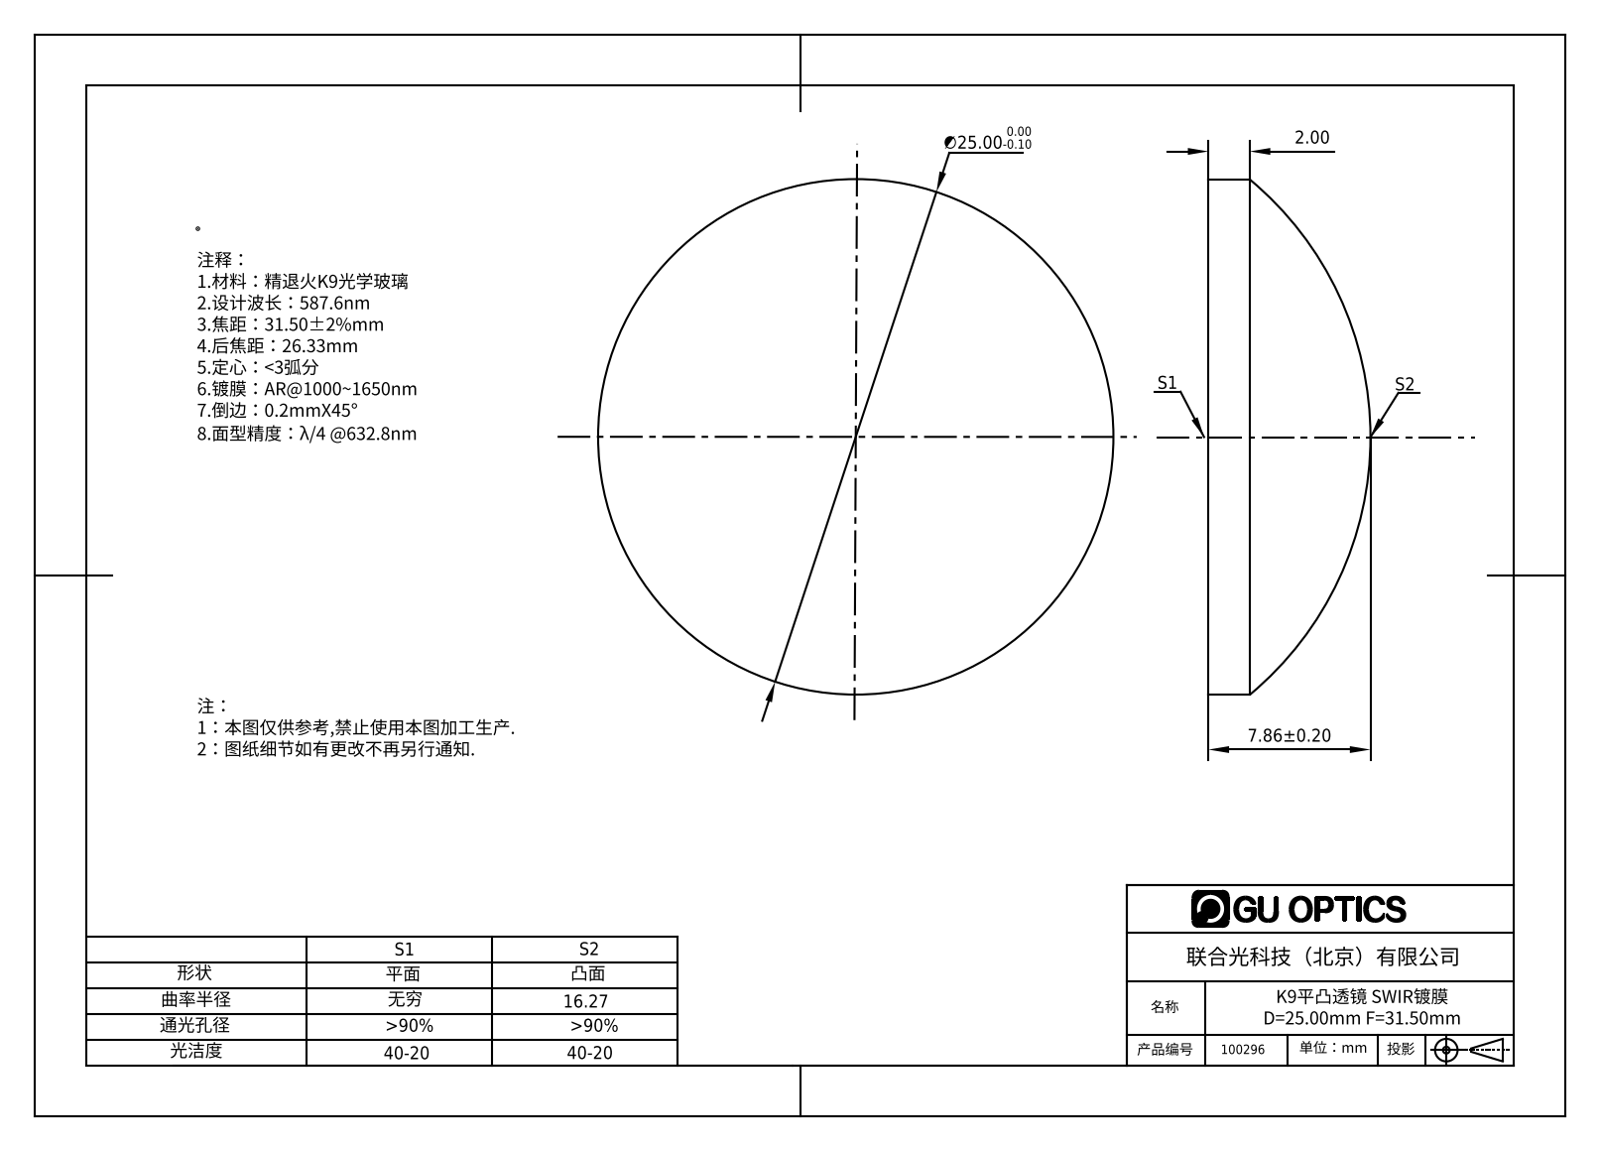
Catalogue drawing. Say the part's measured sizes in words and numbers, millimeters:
The part is named "100124". Its 3-D file was written by "SolidWorks 2016 (AUTOMOTIVE_DESIGN)". It is 1 solid with 5 faces: 1 planar, 2 cylindrical and 2 other. Overall it measures 25 by 25 by 7.86 millimeters. Its volume is 2 525 cubic millimeters and its surface area 1 247 square millimeters. Round bosses or shafts: 1 of diameter 25.
